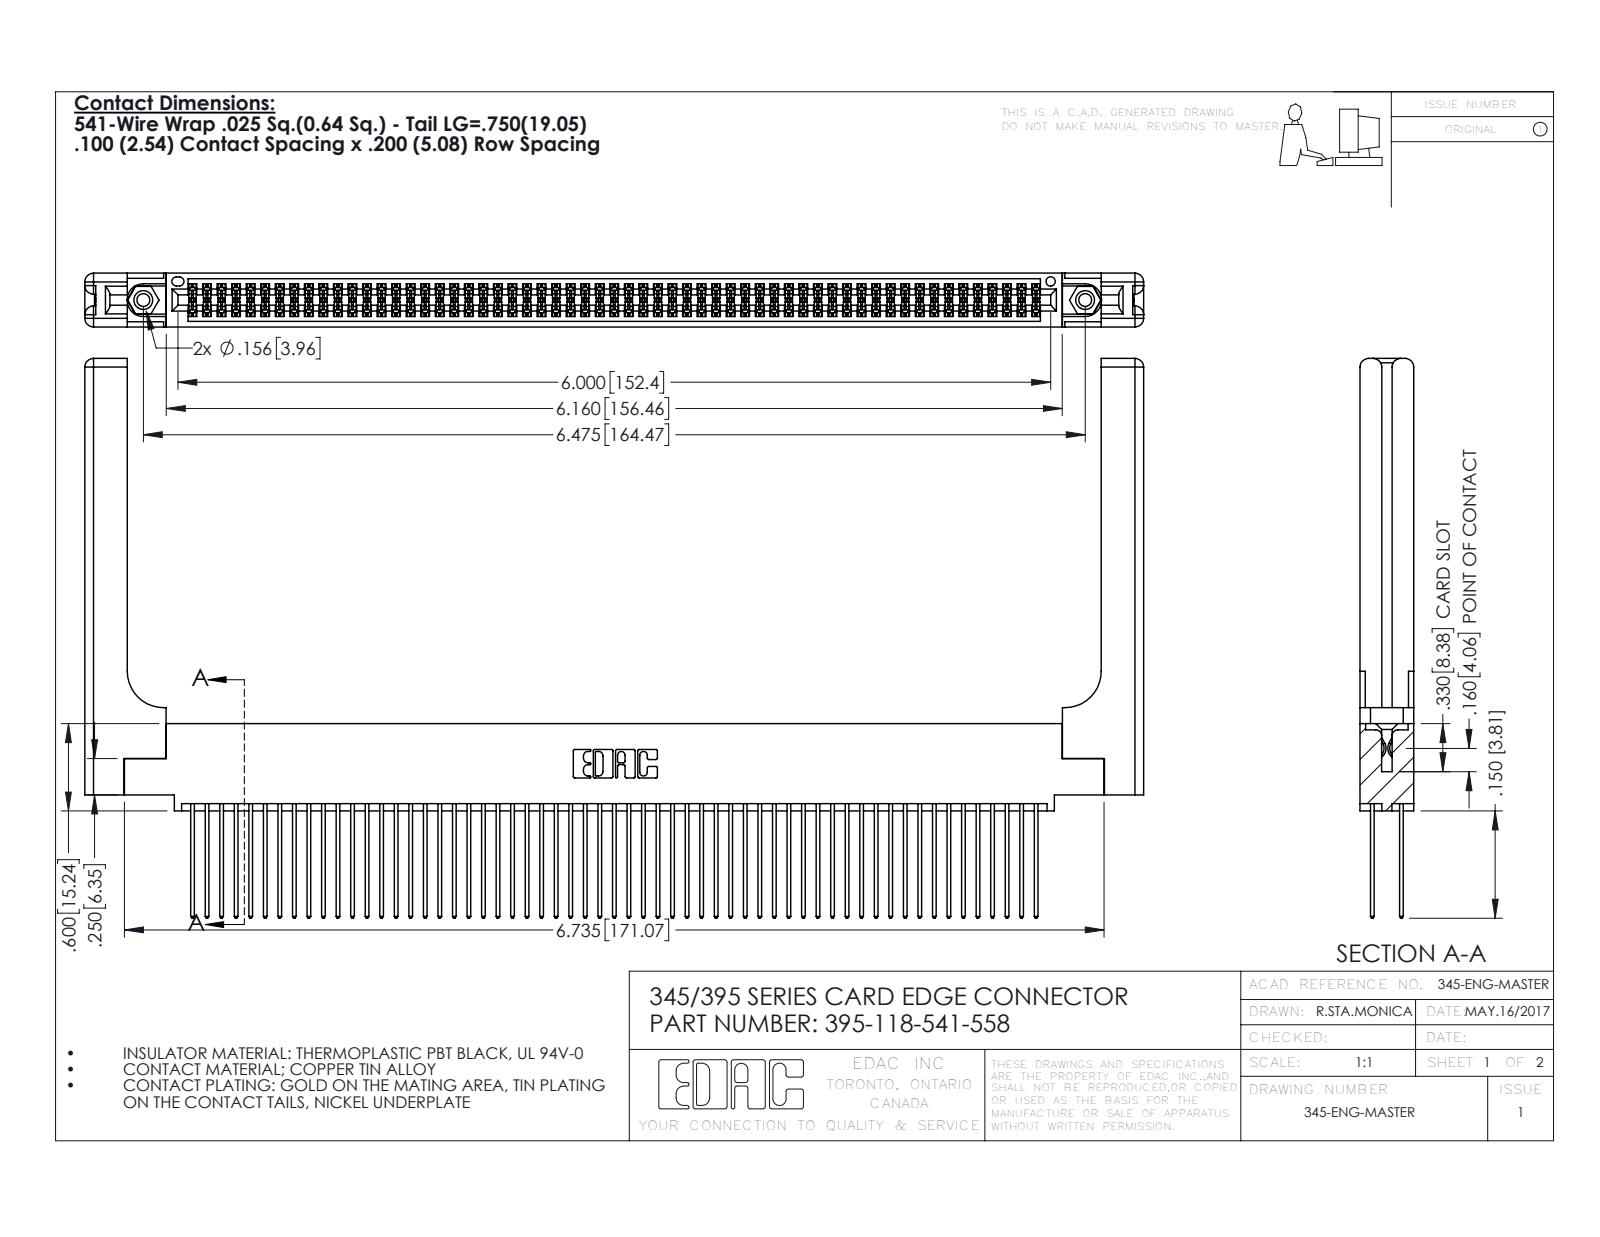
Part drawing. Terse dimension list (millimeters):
name: 395-118-541-558; 345-220-058_345-220-058; 345-250-001_345-250-001-102; 345-292-001_345-293-141 (+1 more)
written by: SolidWorks 2016 (CONFIG_CONTROL_DESIGN)
unit: mm
bodies: 123 solids, 6286 faces (4126 planar, 2100 cylindrical, 60 other)
size: 184.9 × 97.7 × 9.4
volume: 27 200 mm³; area: 36 340 mm²
holes: 2× ⌀2.3, 2× ⌀3.2, 2× ⌀4, 1× ⌀1.6
bosses: 2× ⌀3.9
rounds: 177× R0.2, 118× R0.3, 22× R0.3, 16× R1.5, 6× R0.2, 6× R0.8, 3× R0.7, 2× R0.4
face distances: 1.8, 7.6, 2.5, 6.9, 0.6, 5.1, 9.4, 5.7, 4.4, 3.8
hole spacings: 6.9, 158.5, 164.5
